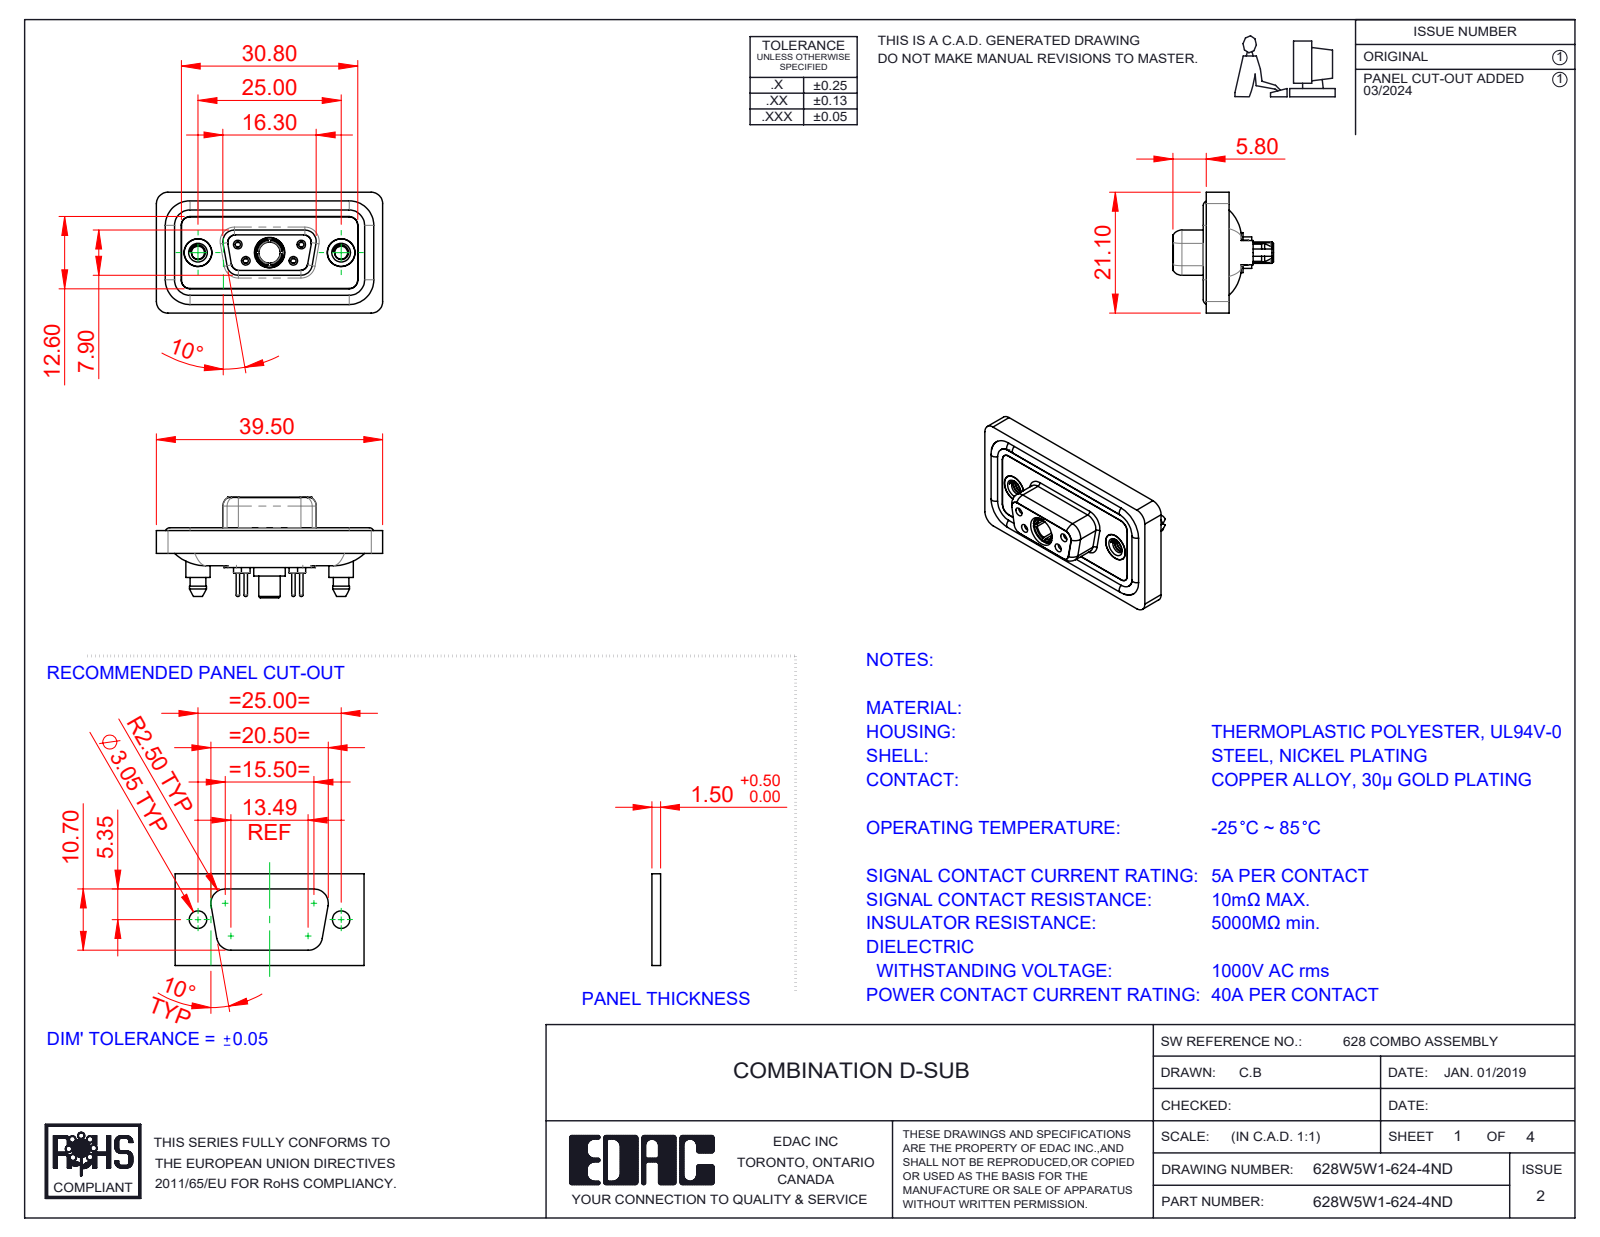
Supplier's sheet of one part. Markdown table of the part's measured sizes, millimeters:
| quantity | value |
| --- | --- |
| part name | 628W5W1-624-4ND; 628Combo Shell Rear_09 Contacts; 628Combo Housing_5W1; 628Combo Threaded Boardlock_D (+5 more) |
| STEP written by | SolidWorks 2023 (CONFIG_CONTROL_DESIGN) |
| units | millimeters |
| bodies | 13 solids, 746 faces (210 planar, 335 cylindrical, 201 other) |
| overall size | 39.5 × 21.1 × 17.55 |
| volume | 4 921 mm³ |
| surface area | 7 985 mm² |
| round holes (diameter × count) | 0.9 × 4, 1.1 × 4, 1.5 × 4, 2 × 4, 4.85 × 3, 1.6 × 2, 1.7 × 2, 2.26 × 2, 4 × 2, 4.05 × 2, 5 × 2, 3.7 × 1 |
| round bosses / shafts (diameter × count) | 1.6 × 6, 2.2 × 4, 0.6 × 4, 5.4 × 2, 4.95 × 2, 4.8 × 2, 4.25 × 2, 5.5 × 1 |
| partial cylindrical surfaces (radius × count) | 1.5 × 24, 2 × 18, 1.6 × 10, 1.35 × 8, 0.25 × 4, 0.5 × 4, 0.6 × 4, 0.65 × 4 |
| main face-to-face distances | 0.4, 2.9, 1.1, 1.8, 1.6, 0.5, 5.65, 7.45, 5.35, 3.6 |
| hole center spacings | 3.16, 5.72, 7.1, 12.5, 18.1, 4.39, 4.4, 8.31 |
